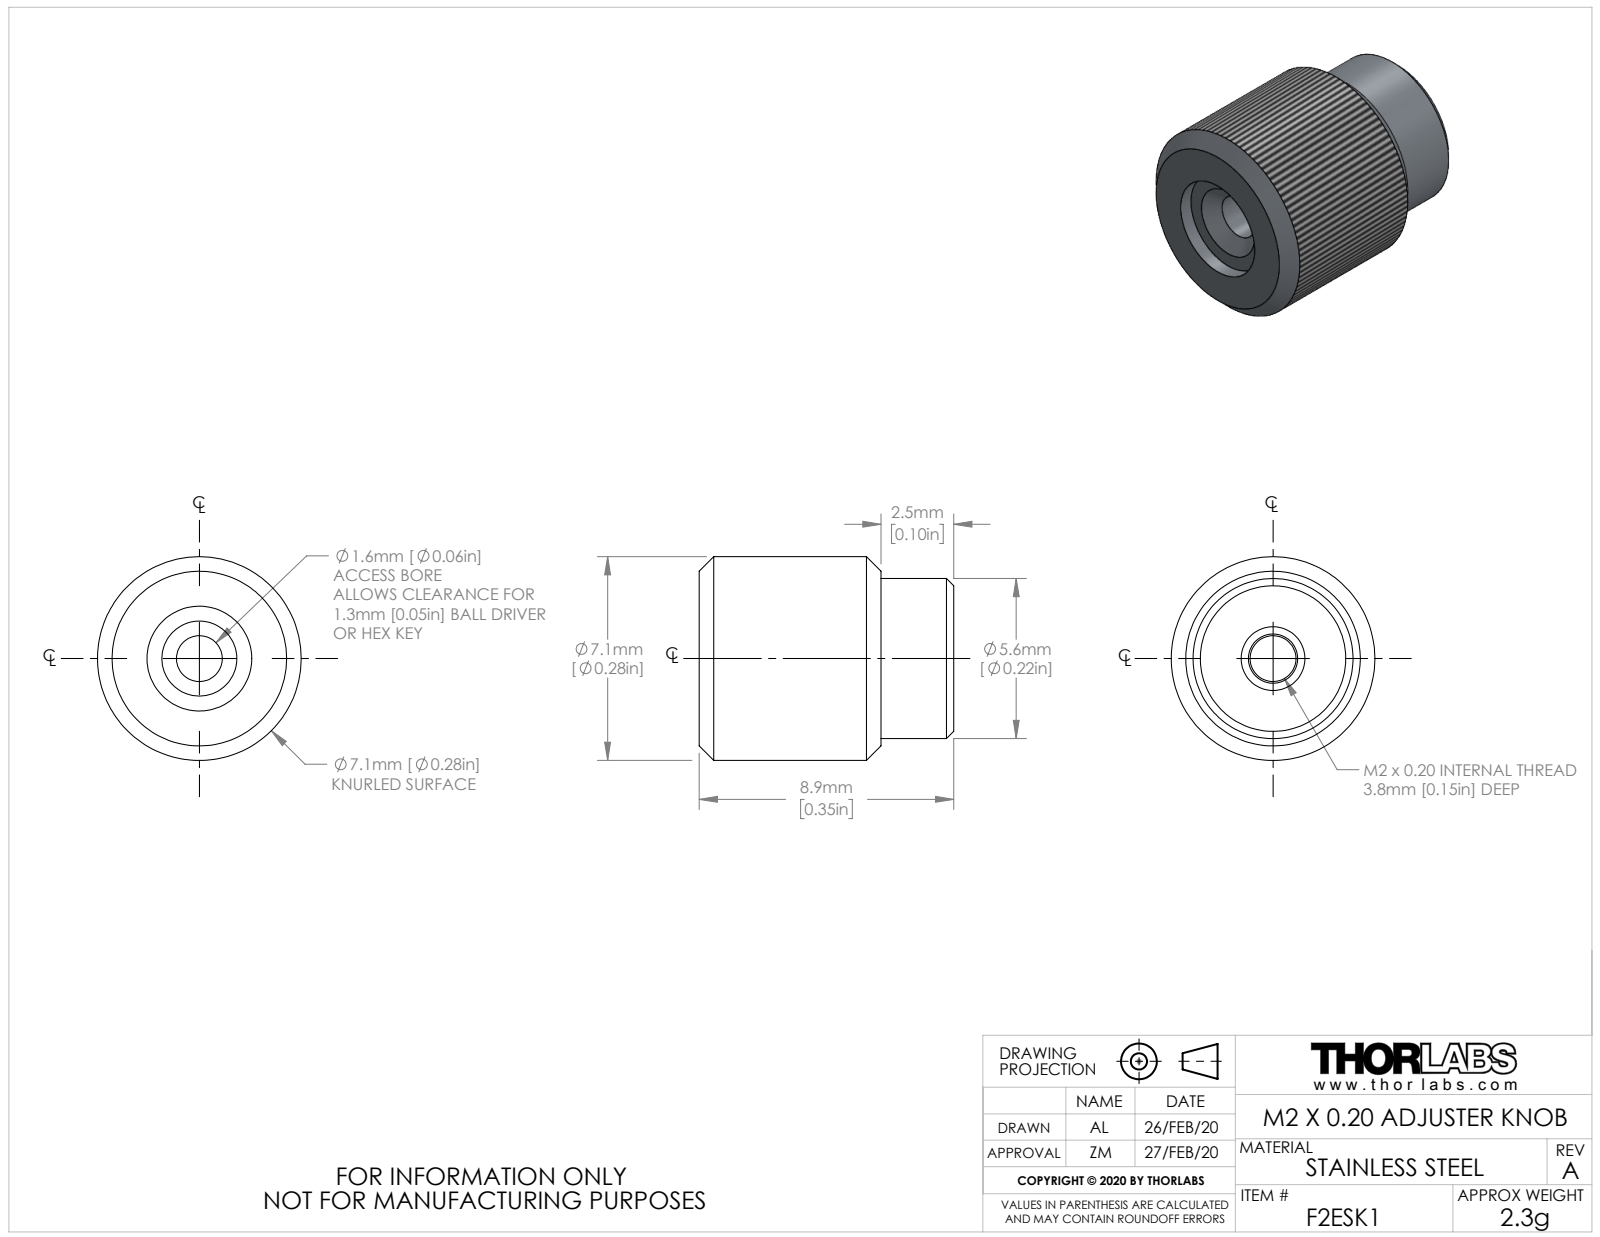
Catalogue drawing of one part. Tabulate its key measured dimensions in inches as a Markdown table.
| quantity | value |
| --- | --- |
| part name | TTN210096-E0W |
| STEP written by | SolidWorks 2018 (AUTOMOTIVE_DESIGN) |
| units | inches |
| bodies | 1 solid, 25 faces (5 planar, 10 cylindrical, 10 other) |
| overall size | 0.35 × 0.28 × 0.28 |
| volume | 0.017 in³ |
| surface area | 0.454 in² |
| round holes (diameter × count) | 0.063 × 1, 0.068 × 1, 0.144 × 1 |
| round bosses / shafts (diameter × count) | 0.28 × 1, 0.22 × 1 |
| main face-to-face distances | 0.35, 0.33, 0.02, 0.1, 0.23, 0.25, 0.15, 0.05, 0.18, 0.2 |
